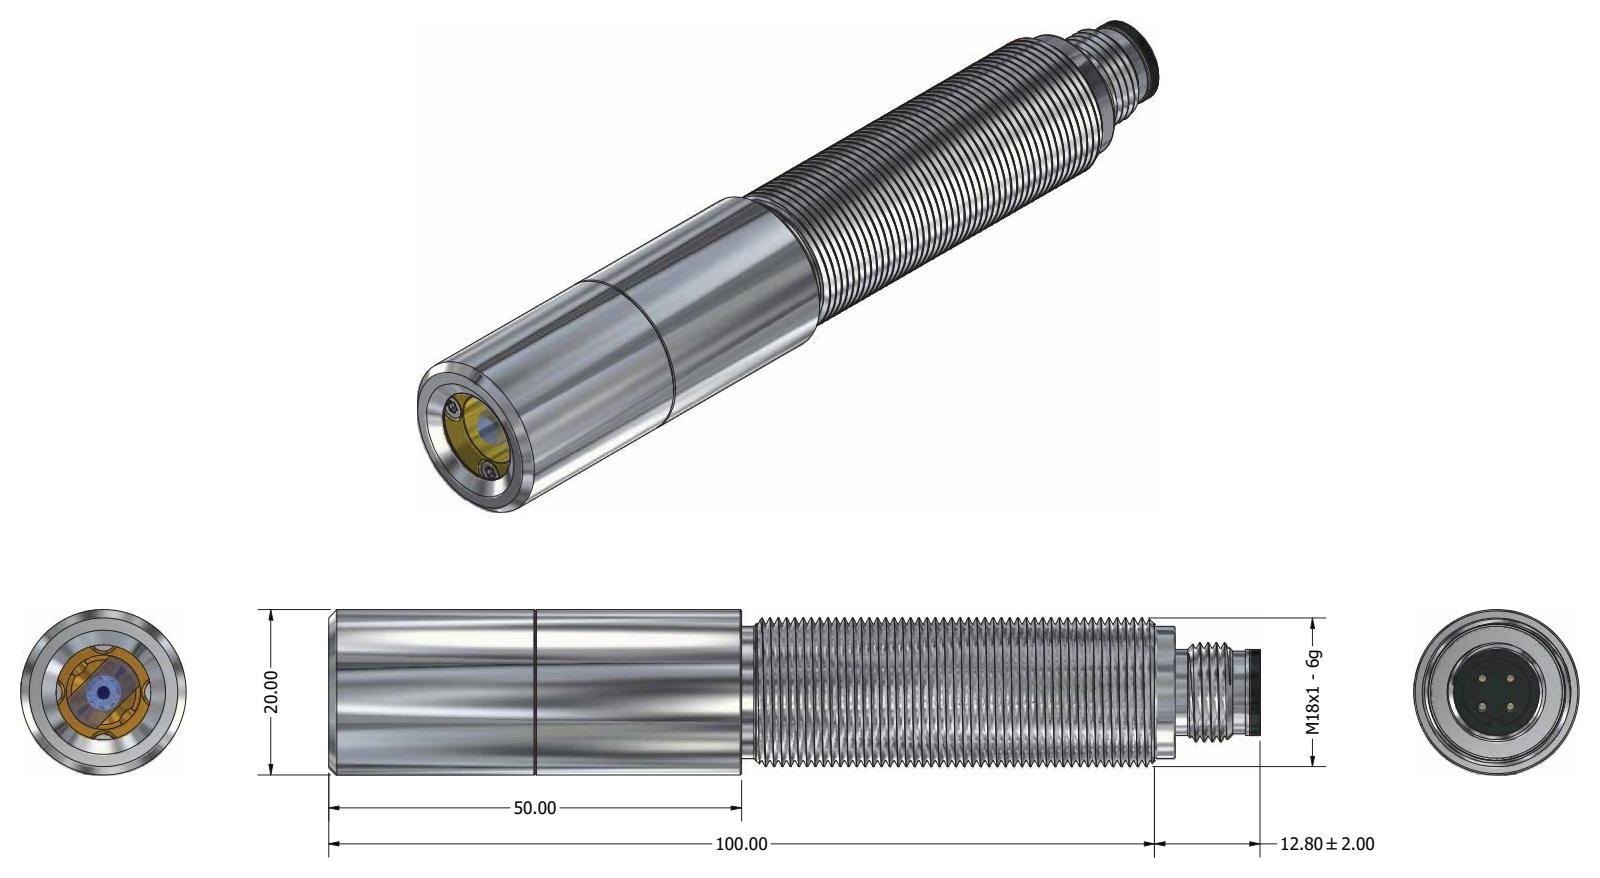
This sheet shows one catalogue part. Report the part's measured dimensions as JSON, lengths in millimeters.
{"part_name": "lwpro_v10; front_v9; back_m18x1_v9; m12_4p_realthread", "step_written_by": "unknown (AUTOMOTIVE_DESIGN)", "units": "millimeters", "bodies": {"solids": 3, "faces": 106, "planar": 17, "cylindrical": 43, "other": 46}, "overall_size": [112.8, 20, 20], "volume_mm3": 13201, "surface_area_mm2": 12929, "round_holes": [[0.75, 4], [8.2, 1], [10.92, 1], [11.5, 1], [13, 1], [16.1, 1], [17.46, 1], [18, 1], [18.4, 1]], "round_bosses_or_shafts": [[1.5, 4], [1, 4], [20, 1], [16, 1], [12, 1], [10.8, 1], [10.4, 1], [10, 1]], "partial_cylinders_radius": [[4.54, 4], [0.9, 1]], "face_to_face_distances": [50, 2.5, 25, 52.5, 100, 10.5, 8, 42, 102.5, 92], "hole_center_spacings": [2.5, 3.54, 5]}
